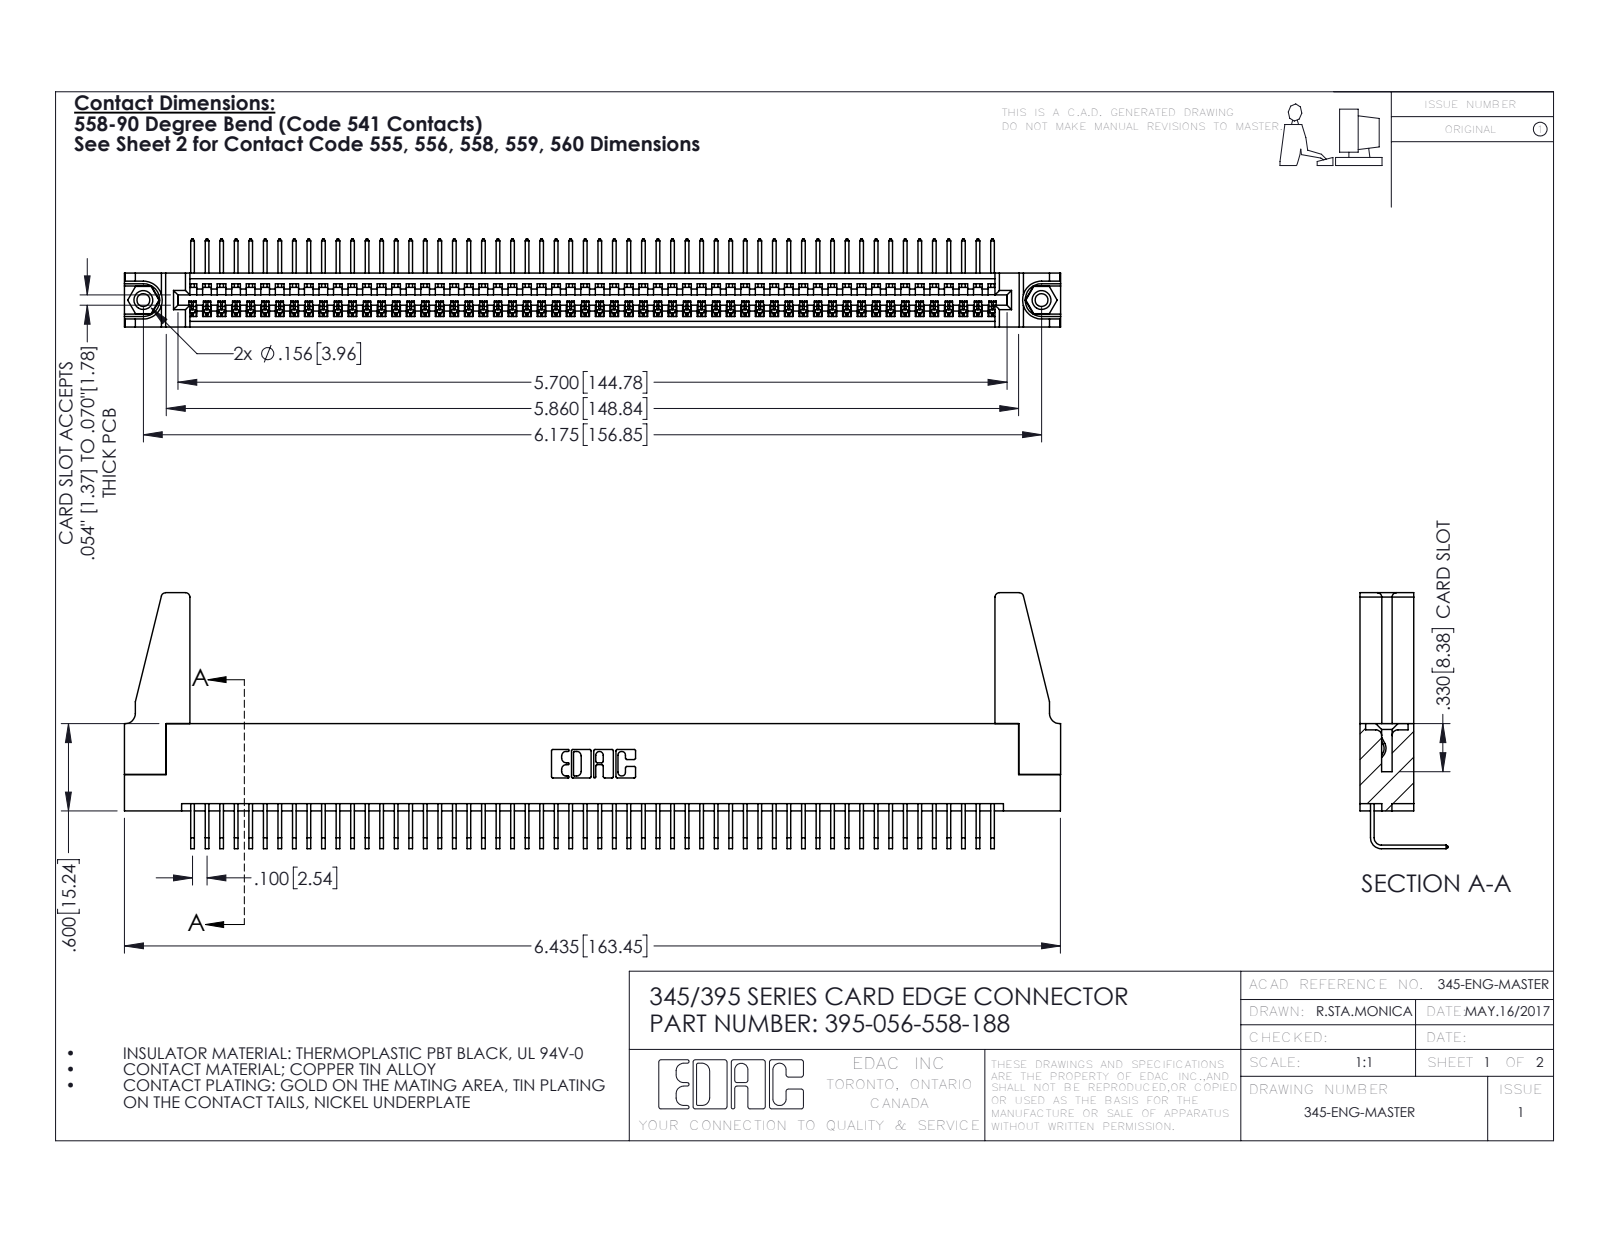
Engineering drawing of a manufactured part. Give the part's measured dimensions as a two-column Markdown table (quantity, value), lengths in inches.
| quantity | value |
| --- | --- |
| part name | 345-292-001_558 Tail - 2; 395-056-558-188; 345-220-078_345-220-088; 345-250-001_345-250-001-102 (+1 more) |
| STEP written by | SolidWorks 2016 (CONFIG_CONTROL_DESIGN) |
| units | inches |
| bodies | 61 solids, 3610 faces (2504 planar, 1090 cylindrical, 16 other) |
| overall size | 6.436 × 1.759 × 0.605 |
| volume | 1.164 in³ |
| surface area | 39.45 in² |
| round holes (diameter × count) | 0.089 × 2, 0.125 × 2, 0.156 × 2, 0.064 × 1 |
| round bosses / shafts (diameter × count) | 0.155 × 2 |
| partial cylindrical surfaces (radius × count) | 0.006 × 112, 0.01 × 22, 0.03 × 8, 0.007 × 6, 0.031 × 6, 0.026 × 3, 0.031 × 2, 0.04 × 2 |
| main face-to-face distances | 0.072, 0.298, 0.37, 0.2, 0.098, 0.272, 0.025, 0.225, 0.149, 0.072 |
| hole center spacings | 0.27, 5.939, 6.175 |
